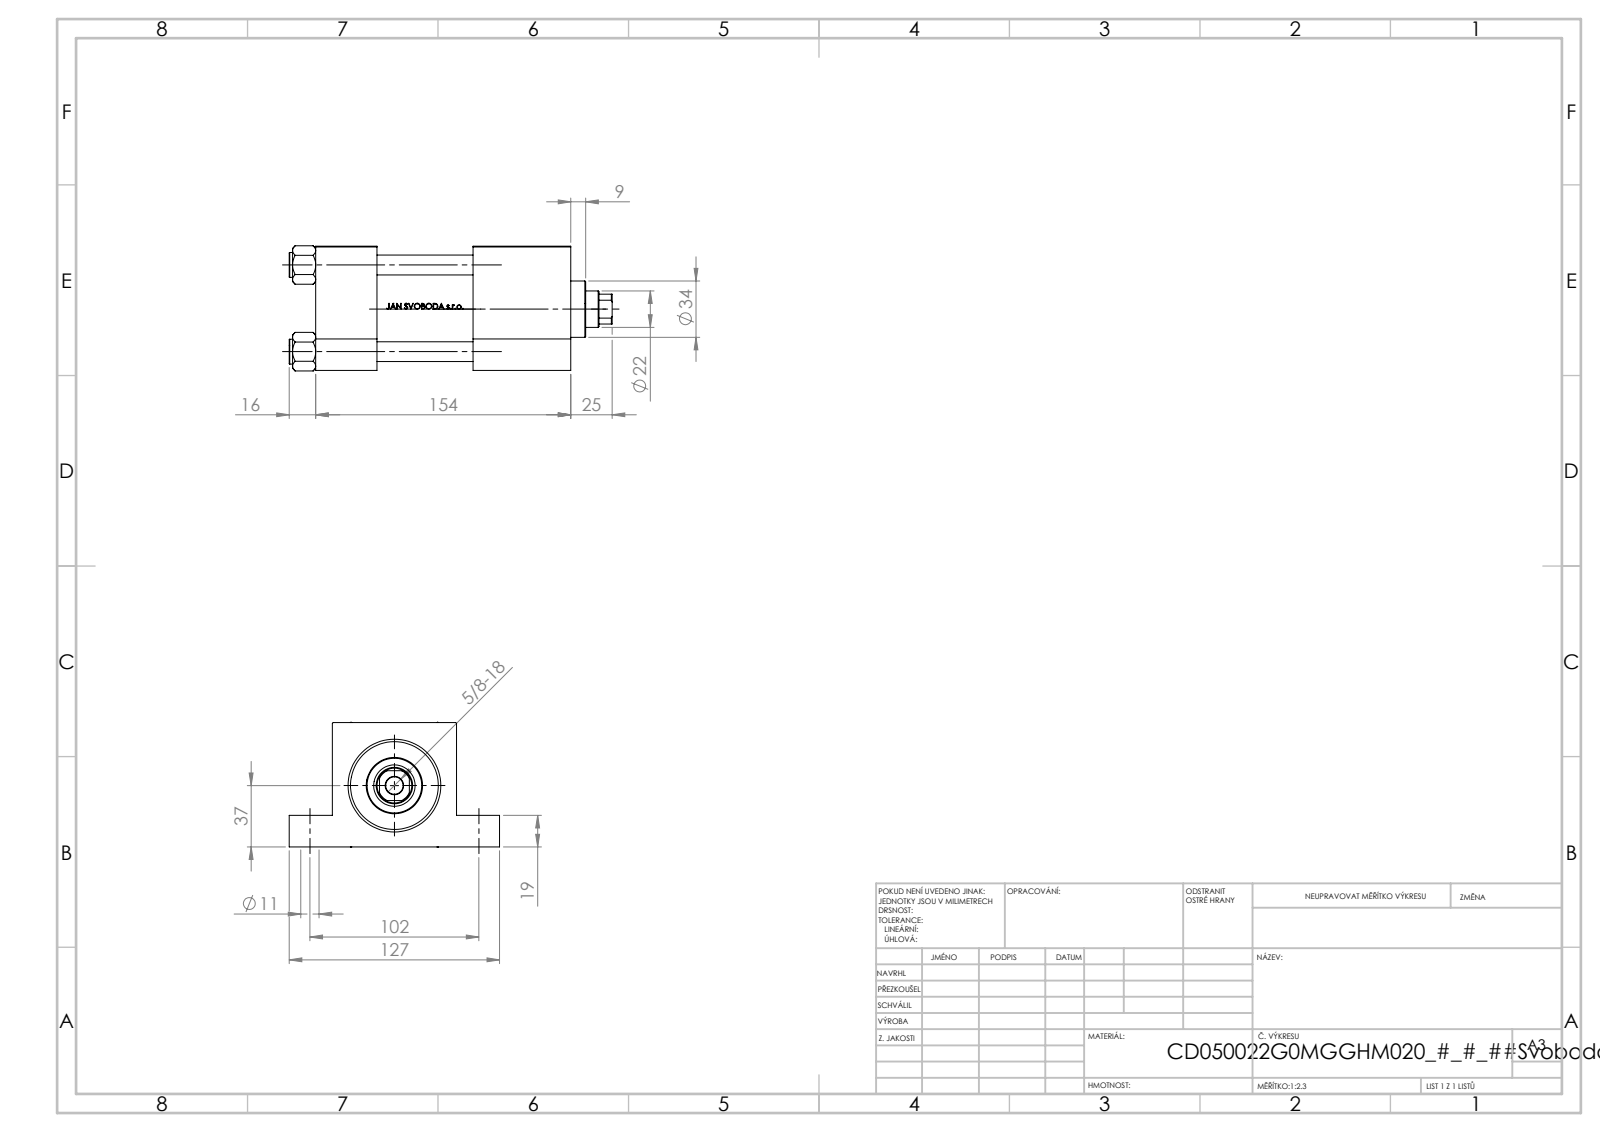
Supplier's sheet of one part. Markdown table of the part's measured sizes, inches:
| quantity | value |
| --- | --- |
| part name | V215CD_G_TYCINKA; V215CD_VC_G; V215CD_VCP_G; V215CD_NUT_M5_G (+1 more) |
| STEP written by | SolidWorks 2019 (CONFIG_CONTROL_DESIGN) |
| units | inches |
| bodies | 11 solids, 1088 faces (432 planar, 124 cylindrical, 532 other) |
| overall size | 7.677 × 5 × 2.974 |
| volume | 46.12 in³ |
| surface area | 247 in² |
| round holes (diameter × count) | 0.433 × 4, 0.472 × 4, 0.276 × 2, 0.825 × 2, 1.181 × 2, 0.413 × 1, 0.866 × 1, 0.984 × 1, 1.614 × 1, 1.969 × 1, 2.087 × 1 |
| round bosses / shafts (diameter × count) | 0.591 × 4, 2.205 × 1, 1.339 × 1 |
| partial cylindrical surfaces (radius × count) | 0.413 × 1 |
| main face-to-face distances | 2.953, 1.457, 6.063, 4.606, 0.748, 2.205, 3.74, 2.283, 2.323, 1.024 |
| hole center spacings | 2.059, 1.442, 1.47, 2.02, 2.072, 2.912, 4.016, 4.384 |
